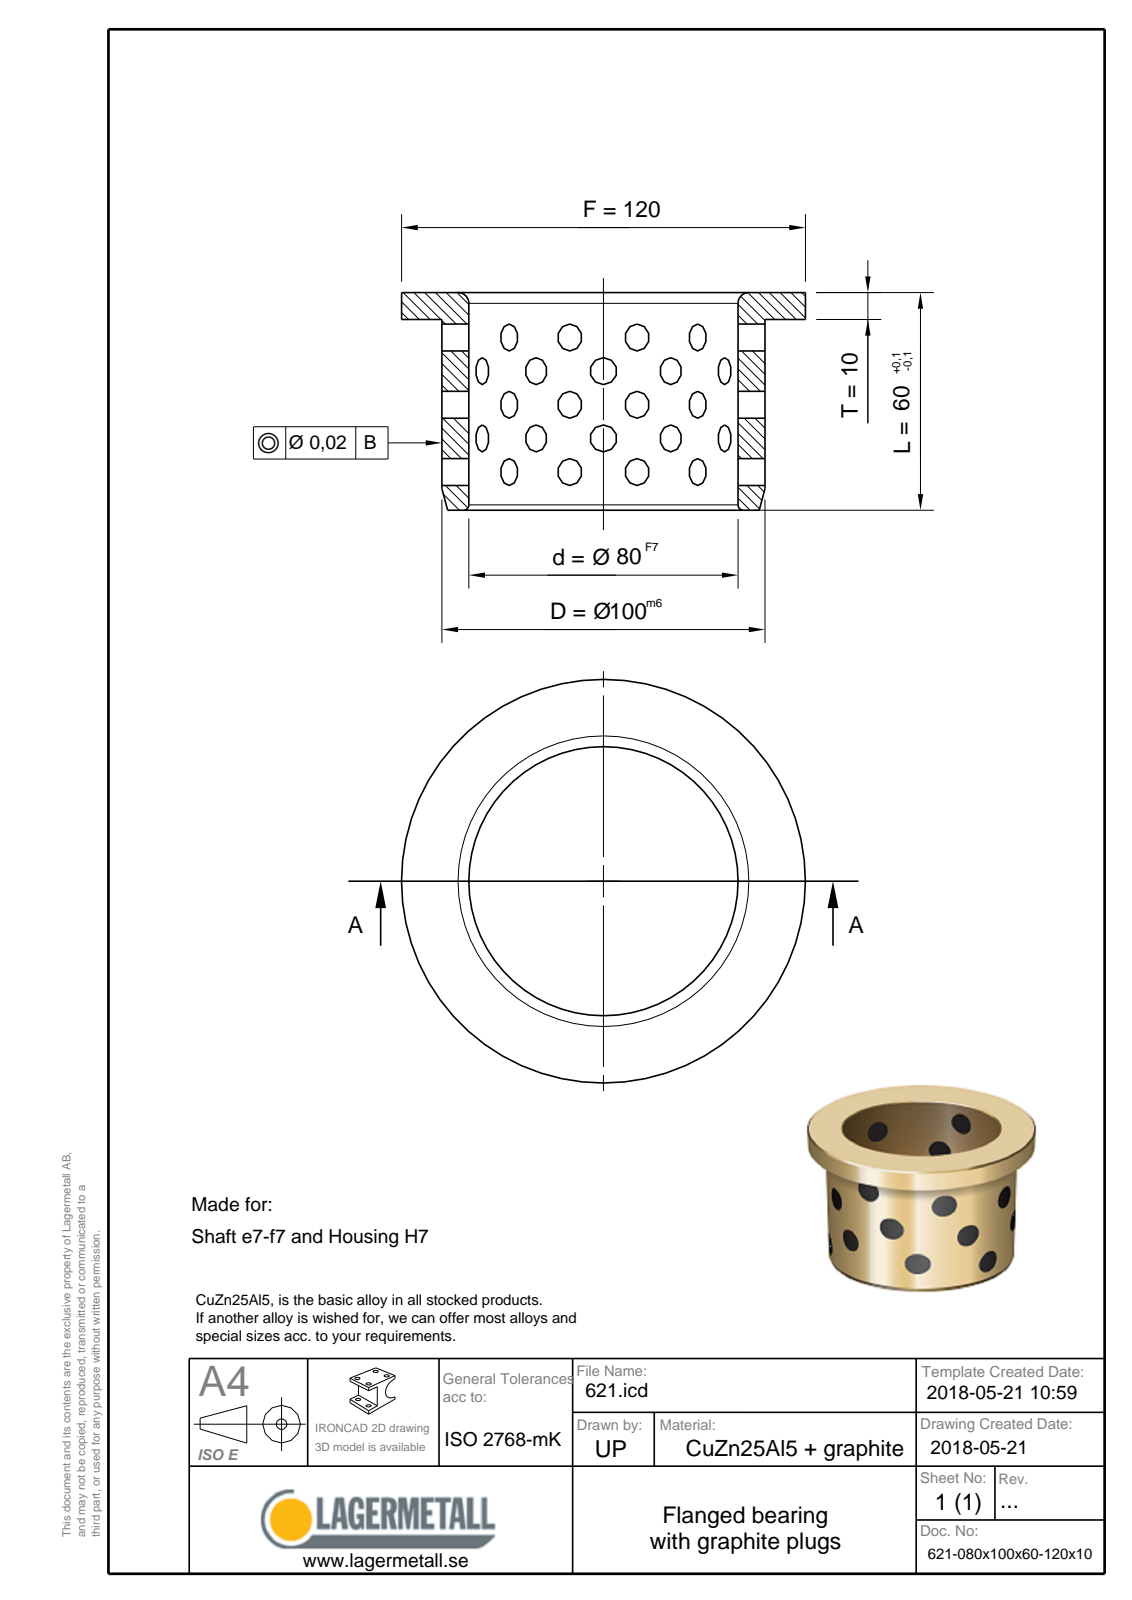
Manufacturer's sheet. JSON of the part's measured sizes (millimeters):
{"part_name": "621-080x100x60-120x10", "step_written_by": "Spatial InterOp 3D (CONFIG_CONTROL_DESIGN)", "units": "millimeters", "bodies": {"solids": 1, "faces": 9, "planar": 3, "cylindrical": 3, "other": 3}, "overall_size": [120, 120, 60], "volume_mm3": 202820, "surface_area_mm2": 46221, "round_holes": [[80, 1]], "round_bosses_or_shafts": [[120, 1], [100, 1]], "face_to_face_distances": [10, 50, 60]}
